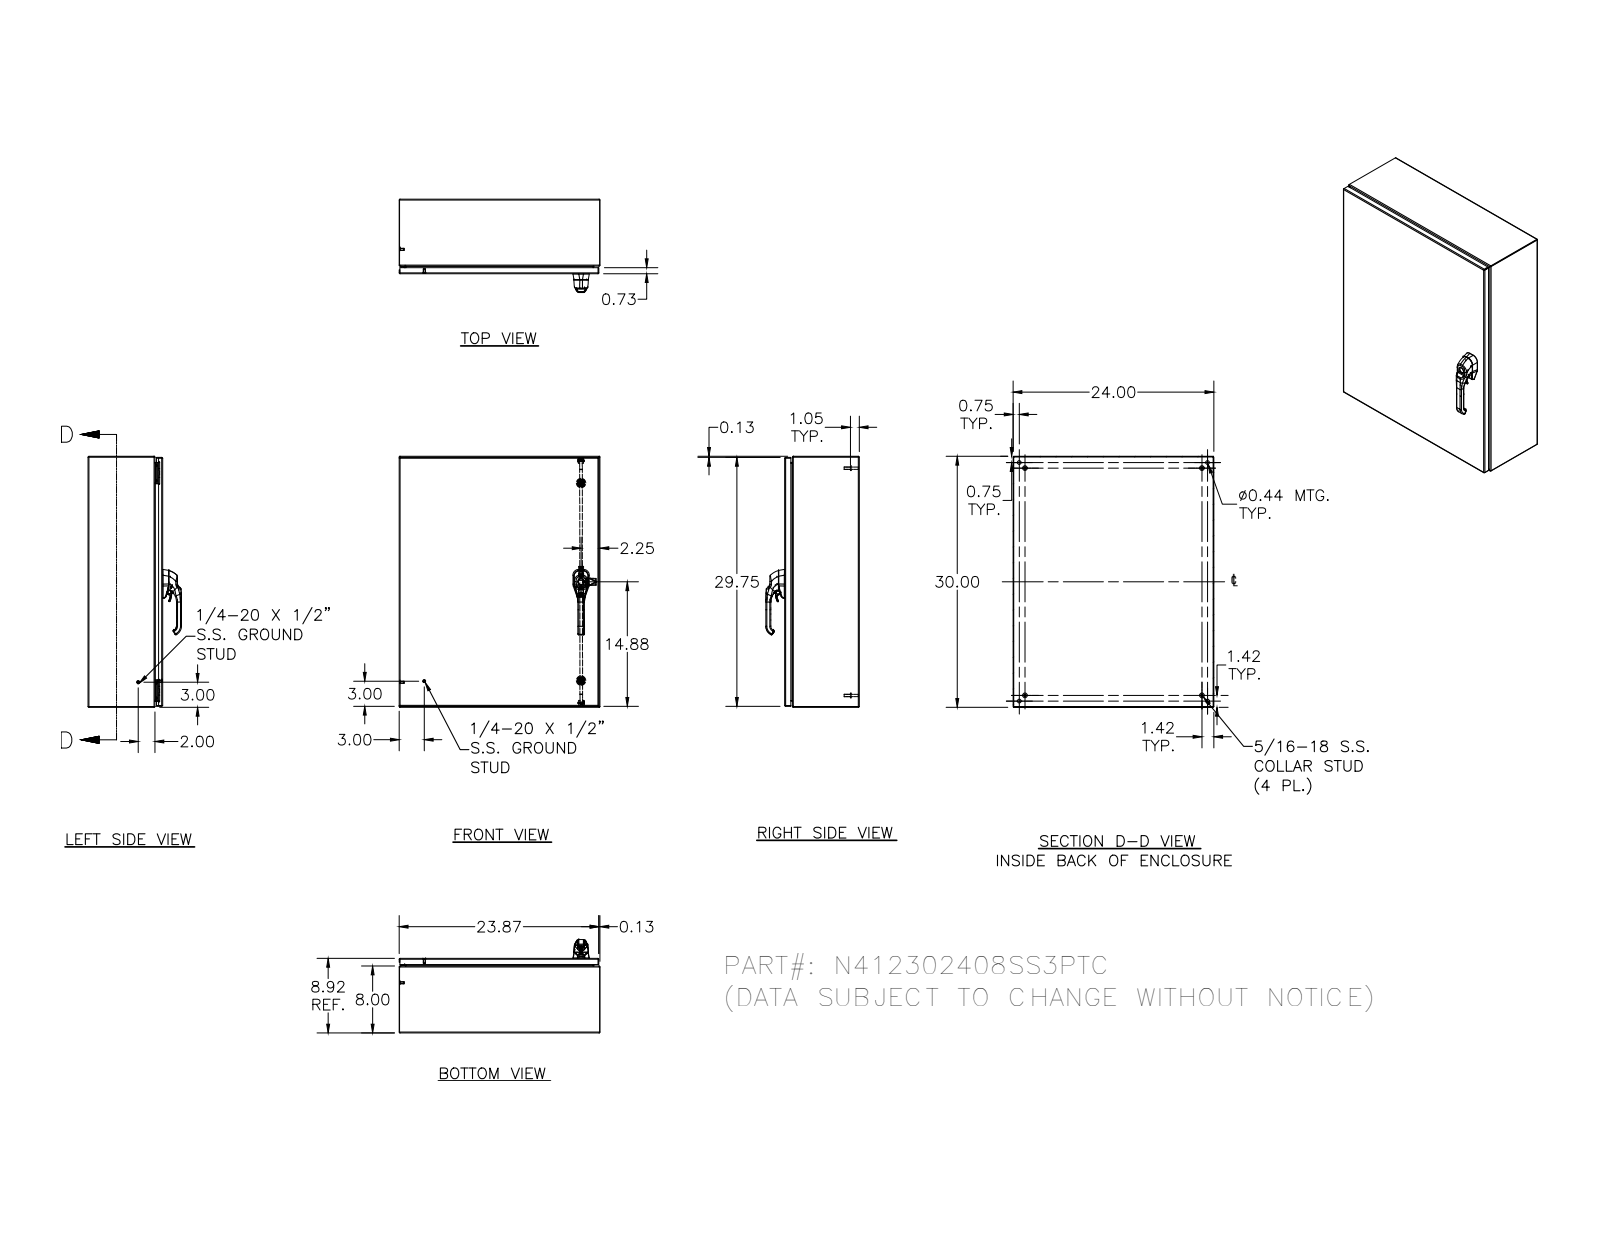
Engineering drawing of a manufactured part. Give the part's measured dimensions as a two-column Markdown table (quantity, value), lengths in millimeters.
| quantity | value |
| --- | --- |
| part name | N412302408SS3PTC; N412302408SS3PTCBKP; N4123024SS3PTCLID; HFW328176 (+8 more) |
| STEP written by | Autodesk Inventor 2011 (AUTOMOTIVE_DESIGN) |
| units | millimeters |
| bodies | 63 solids, 3086 faces (1046 planar, 1117 cylindrical, 923 other) |
| overall size | 762 × 609.6 × 283.6 |
| volume | 3 233 000 mm³ |
| surface area | 3 358 000 mm² |
| round holes (diameter × count) | 4.2 × 5, 2.4 × 4, 3.9 × 4, 4.2 × 4, 4.4 × 4, 4.8 × 4, 5 × 4, 11.1 × 4, 5.4 × 3, 2.7 × 2, 4 × 2, 4.1 × 2 |
| round bosses / shafts (diameter × count) | 6.4 × 10, 6 × 6, 15 × 4, 14.3 × 4, 9.1 × 4, 8.1 × 4, 7.9 × 4, 7.6 × 4 |
| partial cylindrical surfaces (radius × count) | 0.5 × 180, 0.3 × 101, 0.8 × 30, 1.3 × 26, 3 × 23, 0.5 × 21, 2.7 × 20, 0.4 × 18 |
| main face-to-face distances | 1.9, 224.6, 226.5, 222.7, 607.7, 760.1, 605.8, 609.6, 762, 758.2 |
| hole center spacings | 660.3, 580.9, 0.4, 16.8, 41.1, 677.1, 0.5, 12.7 |
